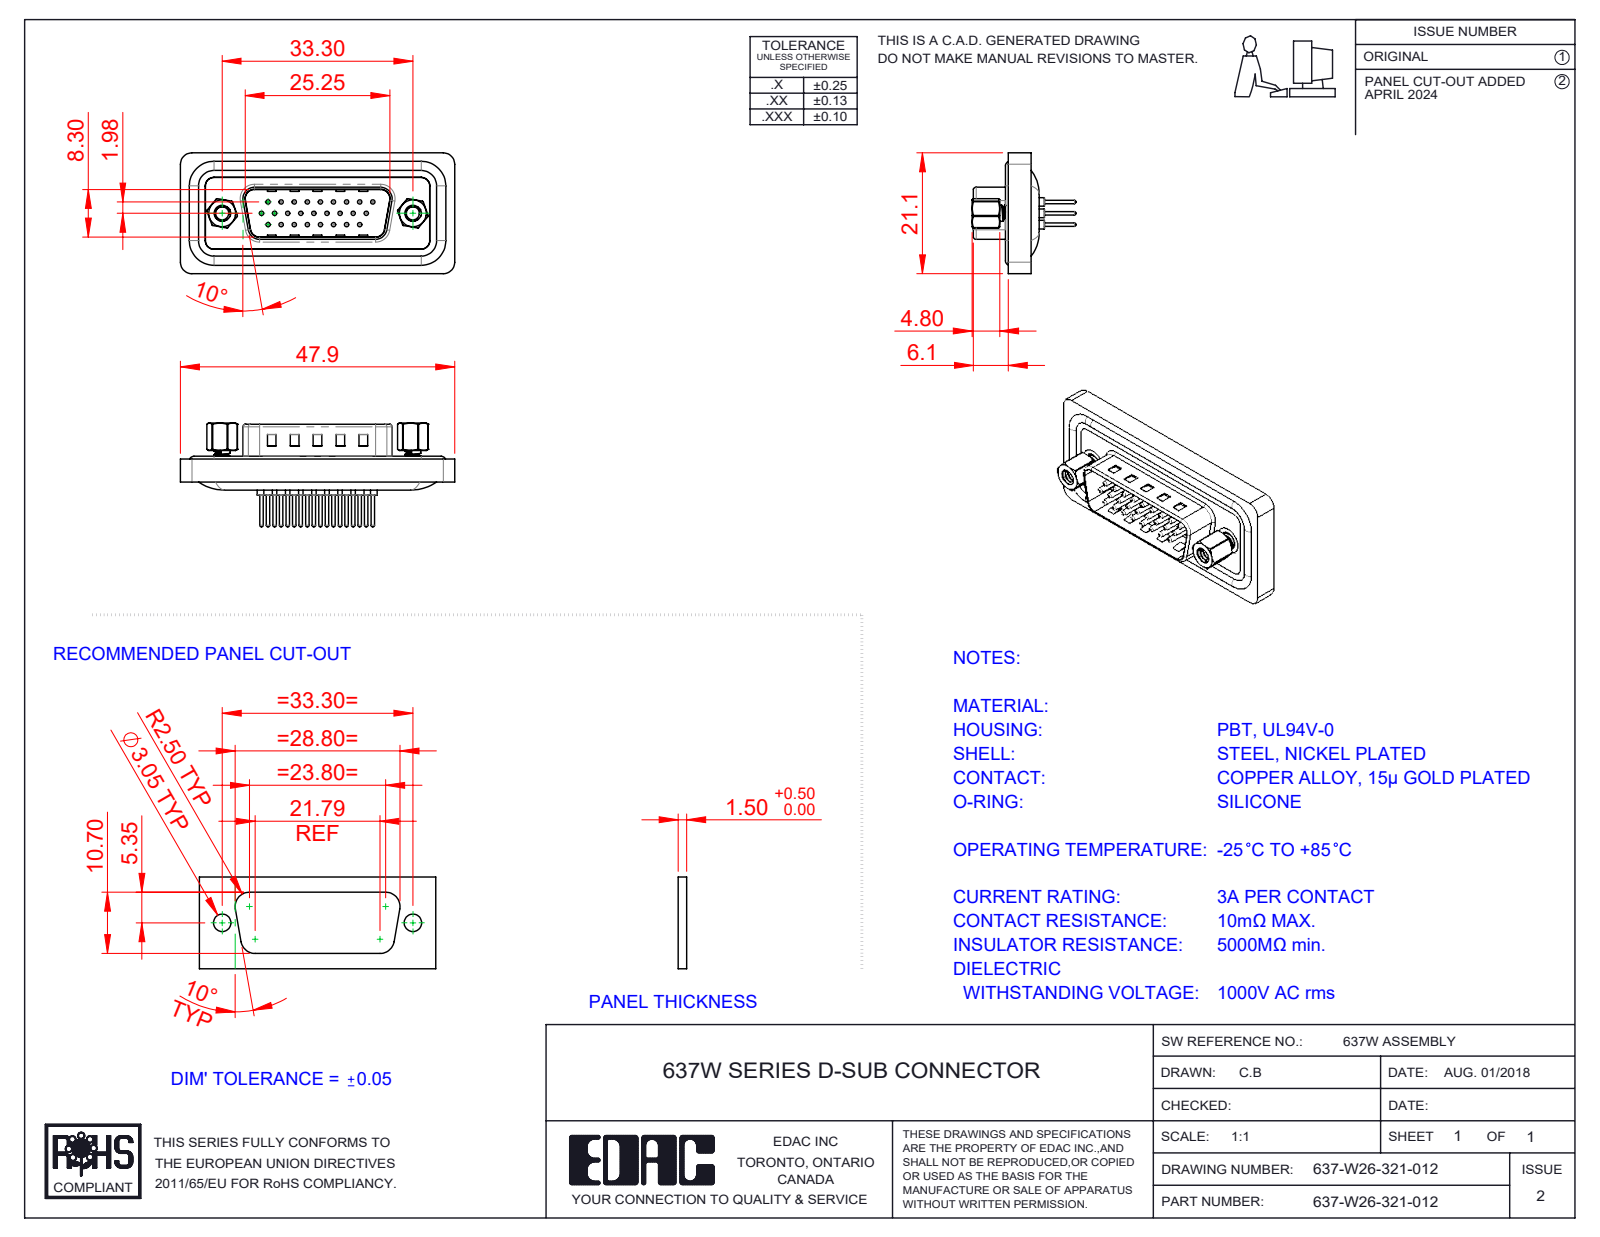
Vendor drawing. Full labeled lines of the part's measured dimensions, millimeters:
Part name (STEP PRODUCT): 637W 4-40 Hex Standoff; 637W 4-40 Threaded Rivet; 637W Waterproof Housing_26 Contacts; 637W Contact Row 3_21 (+5 more)
STEP written by: SolidWorks 2016 (CONFIG_CONTROL_DESIGN)
Units: millimetres
Bodies: 34 solids, 1496 faces (355 planar, 628 cylindrical, 513 other)
Overall size (bounding box): 47.89 × 21.1 × 17.9
Volume: 4 896 mm³ · Surface area: 8 796 mm²
Round holes (diameter × count): ⌀0.75 ×26, ⌀1.5 ×26, ⌀1.6 ×26, ⌀2 ×26, ⌀2.26 ×2, ⌀2.29 ×2, ⌀4 ×2, ⌀4.8 ×2, ⌀5 ×2
Round bosses / shafts (diameter × count): ⌀1.5 ×26, ⌀0.6 ×26, ⌀1.6 ×4, ⌀4.9 ×2, ⌀2.79 ×2, ⌀5 ×1
Partial cylindrical surfaces — rounded edges, fillets, slot ends (radius × count): R2 ×16, R1.5 ×14, R0.5 ×8, R2.7 ×6, R0.9 ×4, R1.6 ×4, R4.3 ×4, R0.4 ×2
Main face-to-face distances: 0.4, 1.6, 1.1, 2.9, 2.5, 0.5, 5.65, 15.45, 0.75, 3.4
Hole centre spacings: 3.96, 2.28, 4.57, 6.05, 2.29, 8.24, 6.86, 6.04
